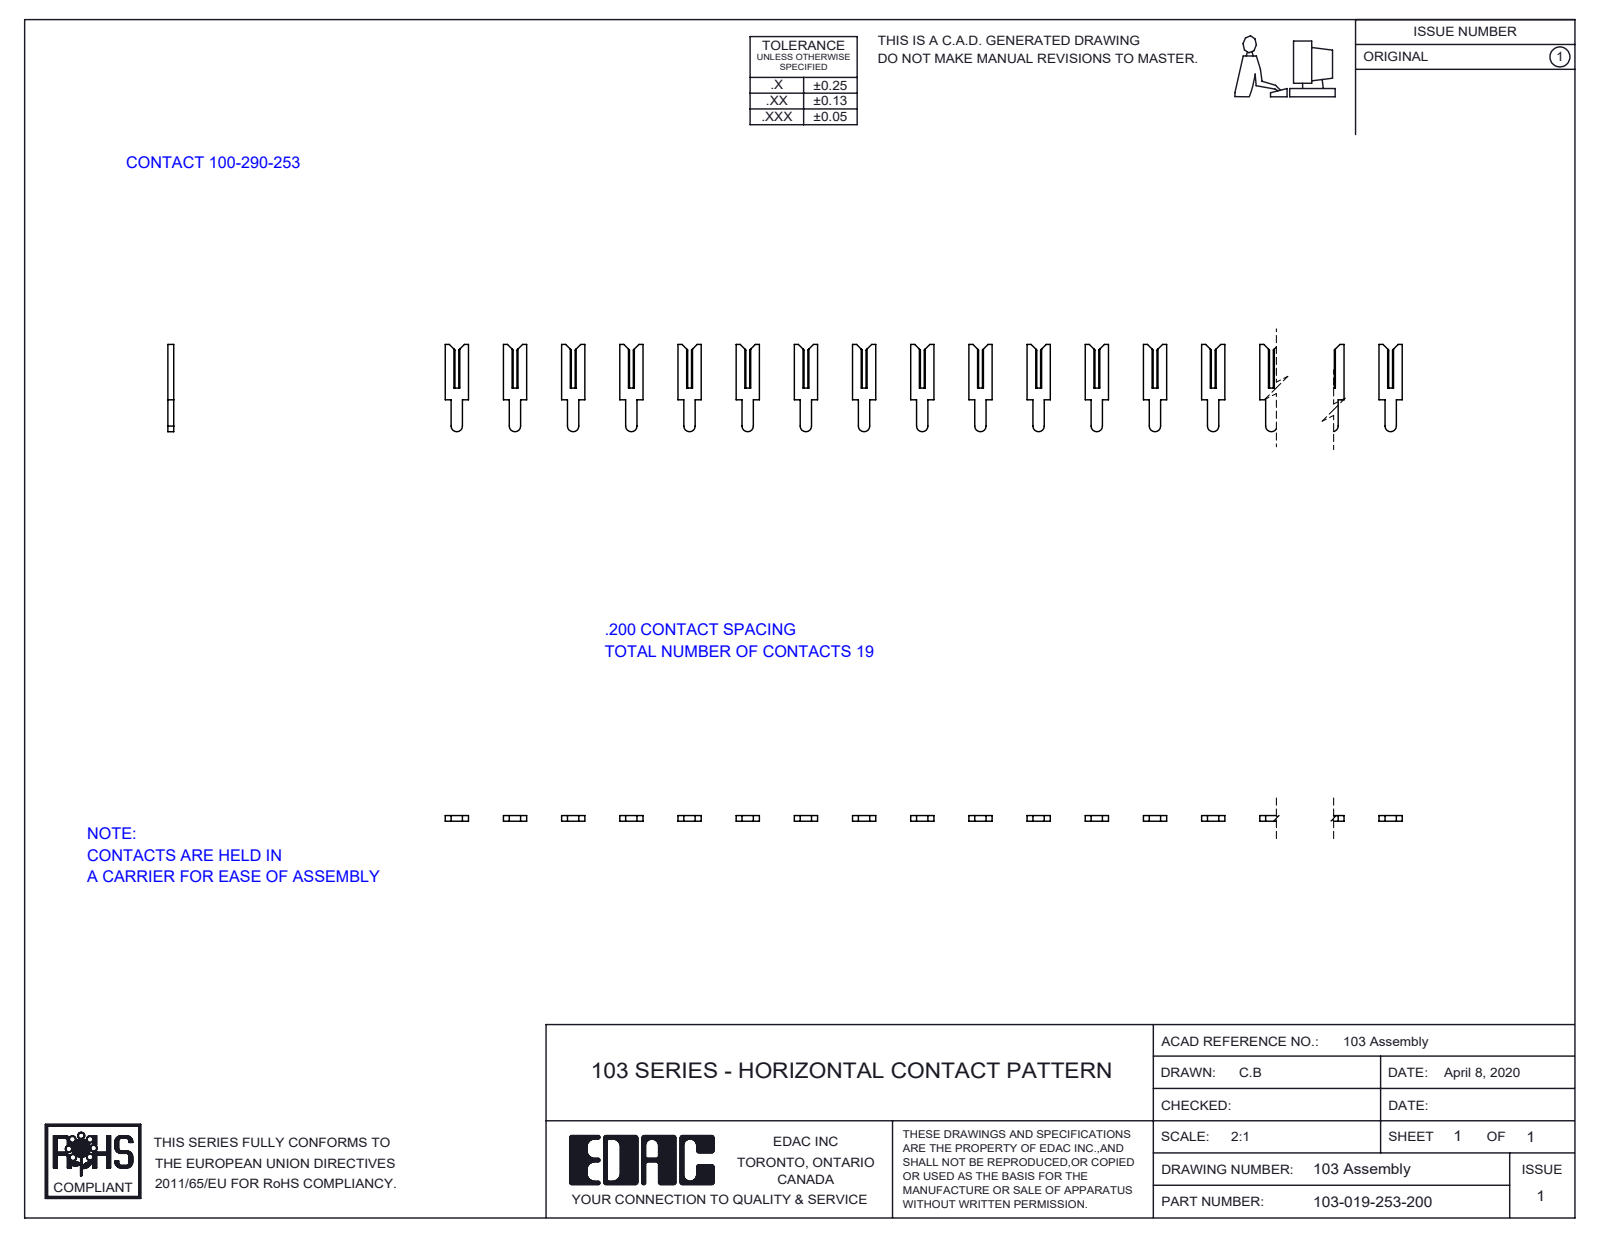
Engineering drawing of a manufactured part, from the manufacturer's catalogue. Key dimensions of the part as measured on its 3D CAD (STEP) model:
Part name (STEP PRODUCT): 100-290-001_100-290-253; 103-019-253-200
STEP written by: SolidWorks 2016 (CONFIG_CONTROL_DESIGN)
Units: inches
Bodies: 19 solids, 380 faces (361 planar, 19 cylindrical, 0 other)
Overall size (bounding box): 3.68 × 0.3 × 0.02
Volume: 0.006 in³ · Surface area: 1.013 in²
Partial cylindrical surfaces — rounded edges, fillets, slot ends (radius × count): R0.019 ×19
Main face-to-face distances: 0.02, 0.2, 0.4, 0.141, 0.6, 0.8, 0.283, 0.848, 0.99, 0.707
